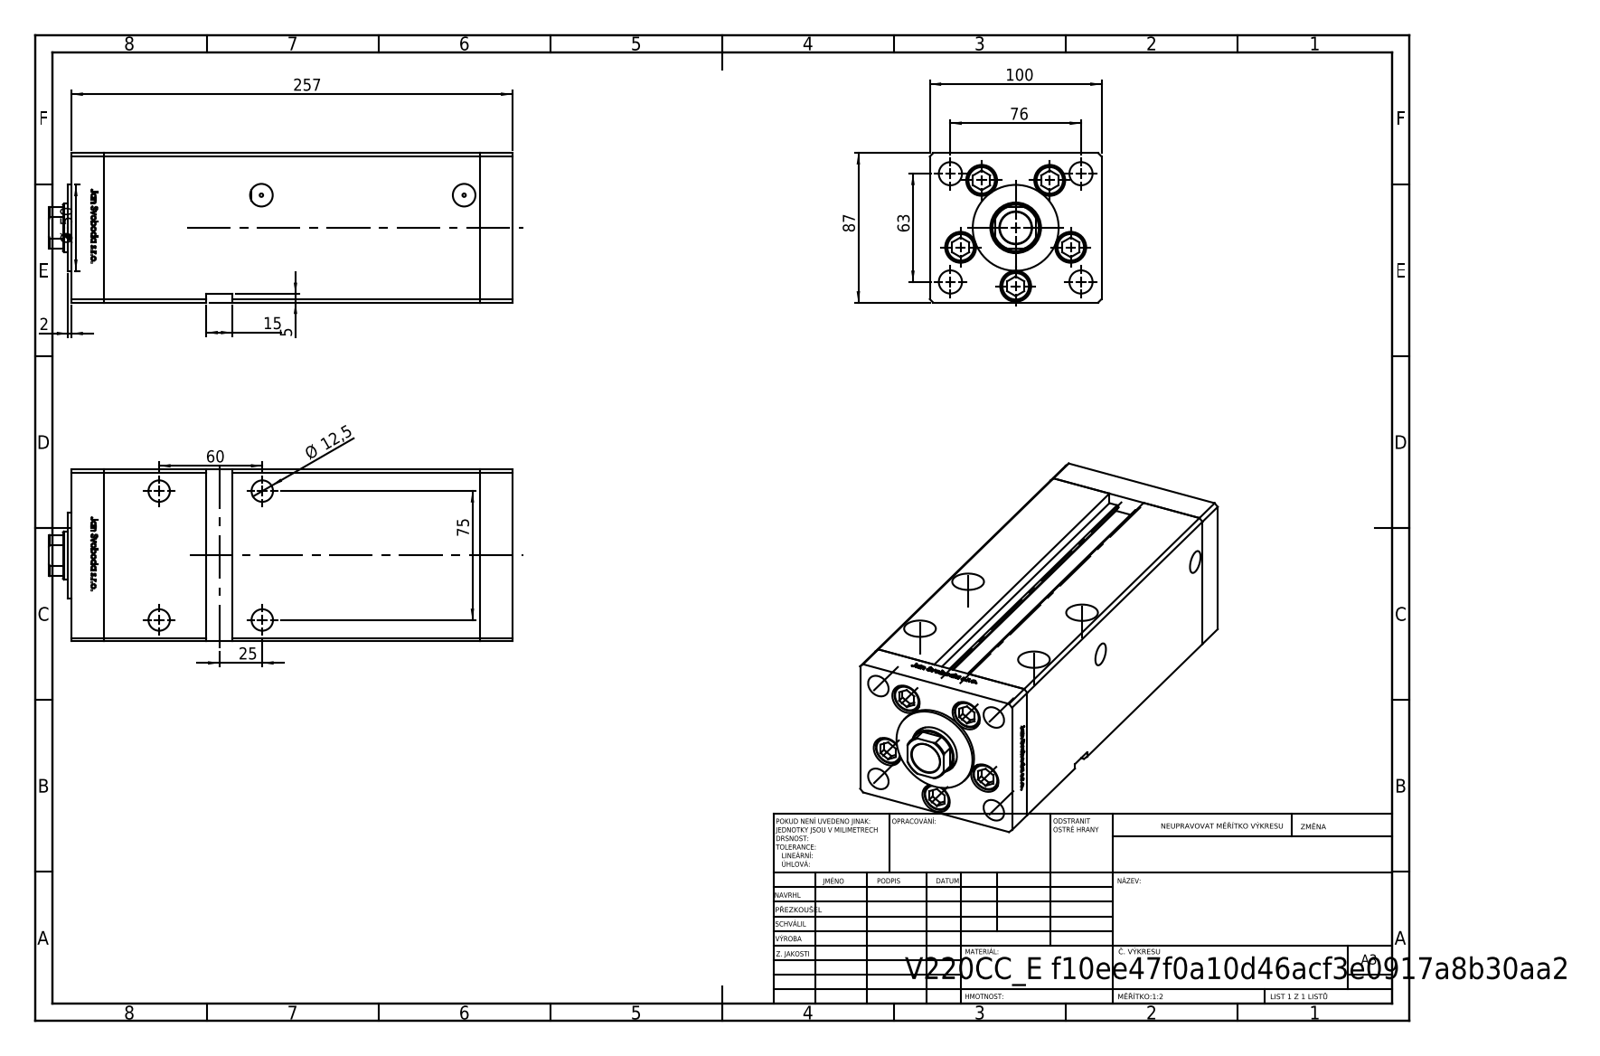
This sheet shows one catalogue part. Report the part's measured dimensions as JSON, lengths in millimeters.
{"part_name": "V220C_VC_E; ALLEN BOLT; V220C BACK_E; V220C_E MIDDLE (+1 more)", "step_written_by": "SolidWorks 2019 (CONFIG_CONTROL_DESIGN)", "units": "millimeters", "bodies": {"solids": 14, "faces": 1214, "planar": 475, "cylindrical": 165, "other": 574}, "overall_size": [269.5, 100, 87], "volume_mm3": 1866000, "surface_area_mm2": 265229, "round_holes": [[13.5, 11], [18, 5], [18.5, 5], [12.5, 4], [2, 2], [13.16, 2], [28, 1], [29.5, 1]], "round_bosses_or_shafts": [[17, 5], [8, 5], [50, 1]], "partial_cylinders_radius": [[0.93, 2], [13.5, 1]], "face_to_face_distances": [100, 87, 19, 218.5, 237.5, 34.25, 256.5, 15.25, 203.25, 222.25], "hole_center_spacings": [34, 18.59, 39.64, 49.36, 57.95, 21.03, 38.08, 39.27]}
